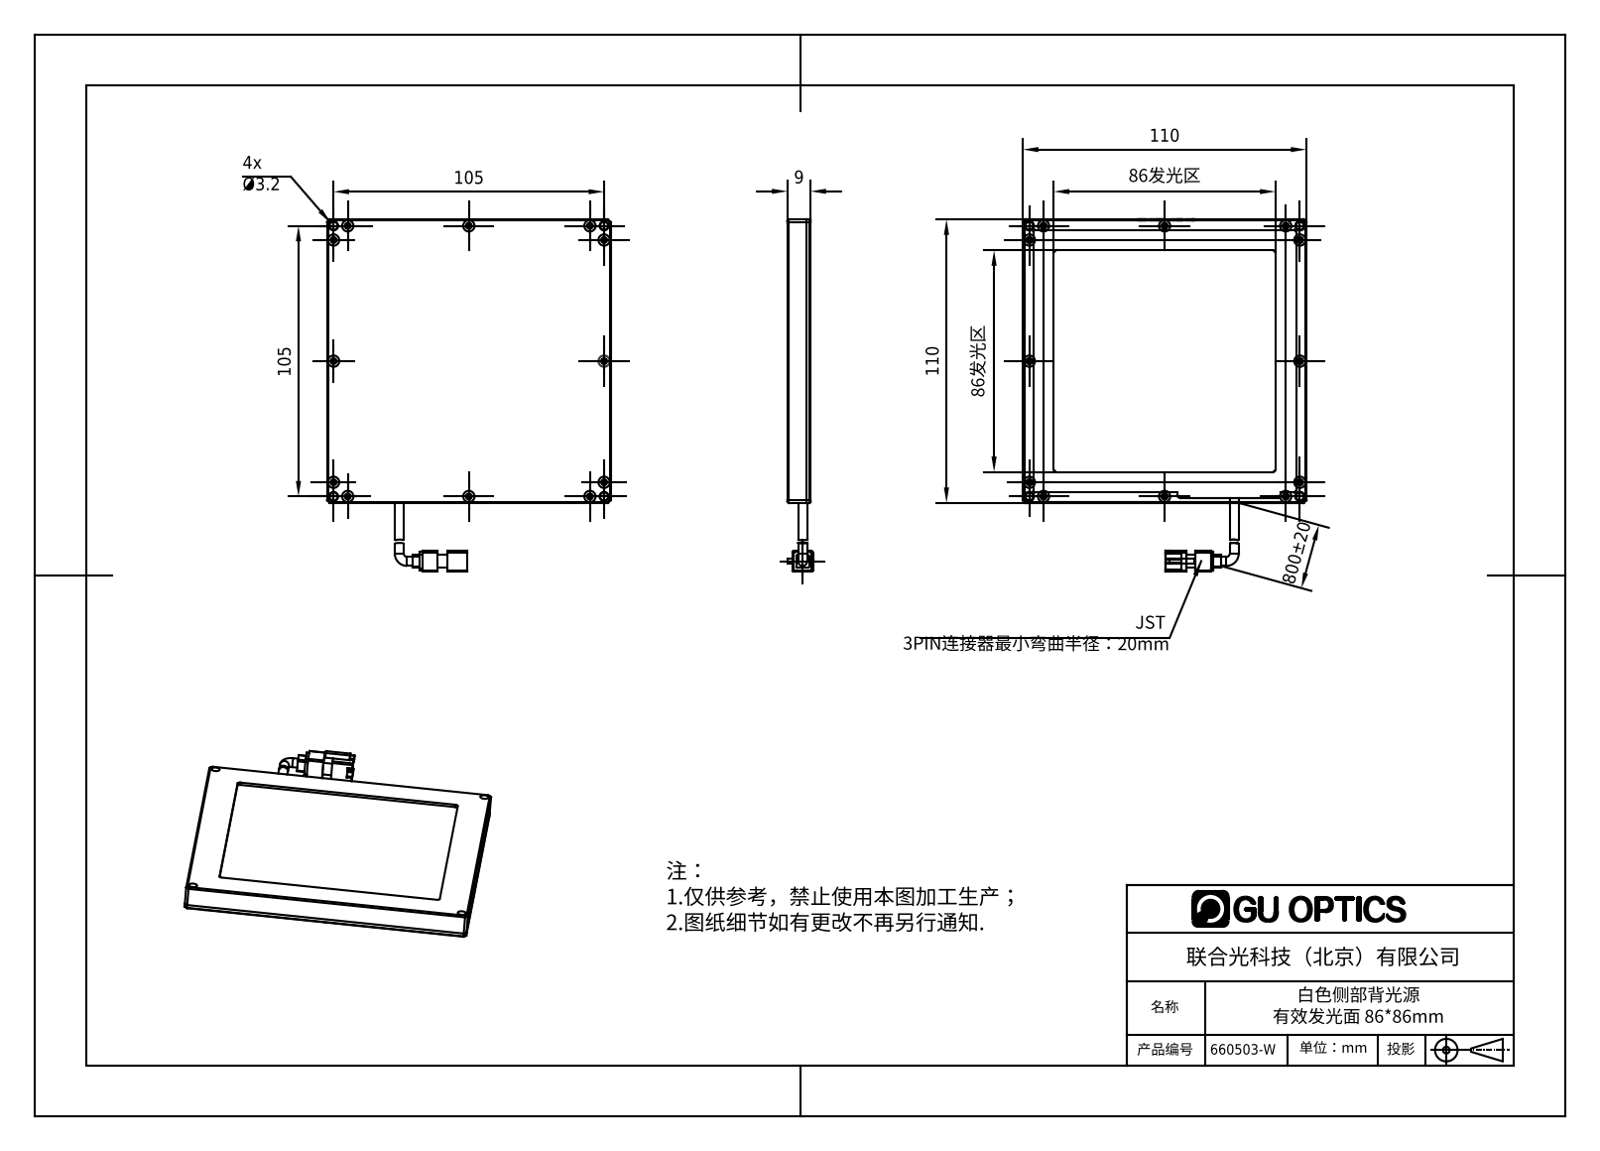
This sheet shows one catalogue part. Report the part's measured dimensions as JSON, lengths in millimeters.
{"part_name": "660503-W", "step_written_by": "SolidWorks 2016 (AUTOMOTIVE_DESIGN)", "units": "millimeters", "bodies": {"solids": 5, "faces": 415, "planar": 184, "cylindrical": 121, "other": 110}, "overall_size": [136.69, 110, 10], "volume_mm3": 69130, "surface_area_mm2": 61430, "round_holes": [[1.6, 12], [2, 12], [2.2, 12], [3.2, 4], [3.5, 4]], "round_bosses_or_shafts": [[3.5, 2]], "partial_cylinders_radius": [[1, 14], [0.5, 8]], "face_to_face_distances": [4, 8, 6.5, 1.5, 2.5, 1, 5, 9, 7.5, 102], "hole_center_spacings": [105, 5.5, 47, 52.5, 52.79, 99.5, 99.65, 105.14]}
